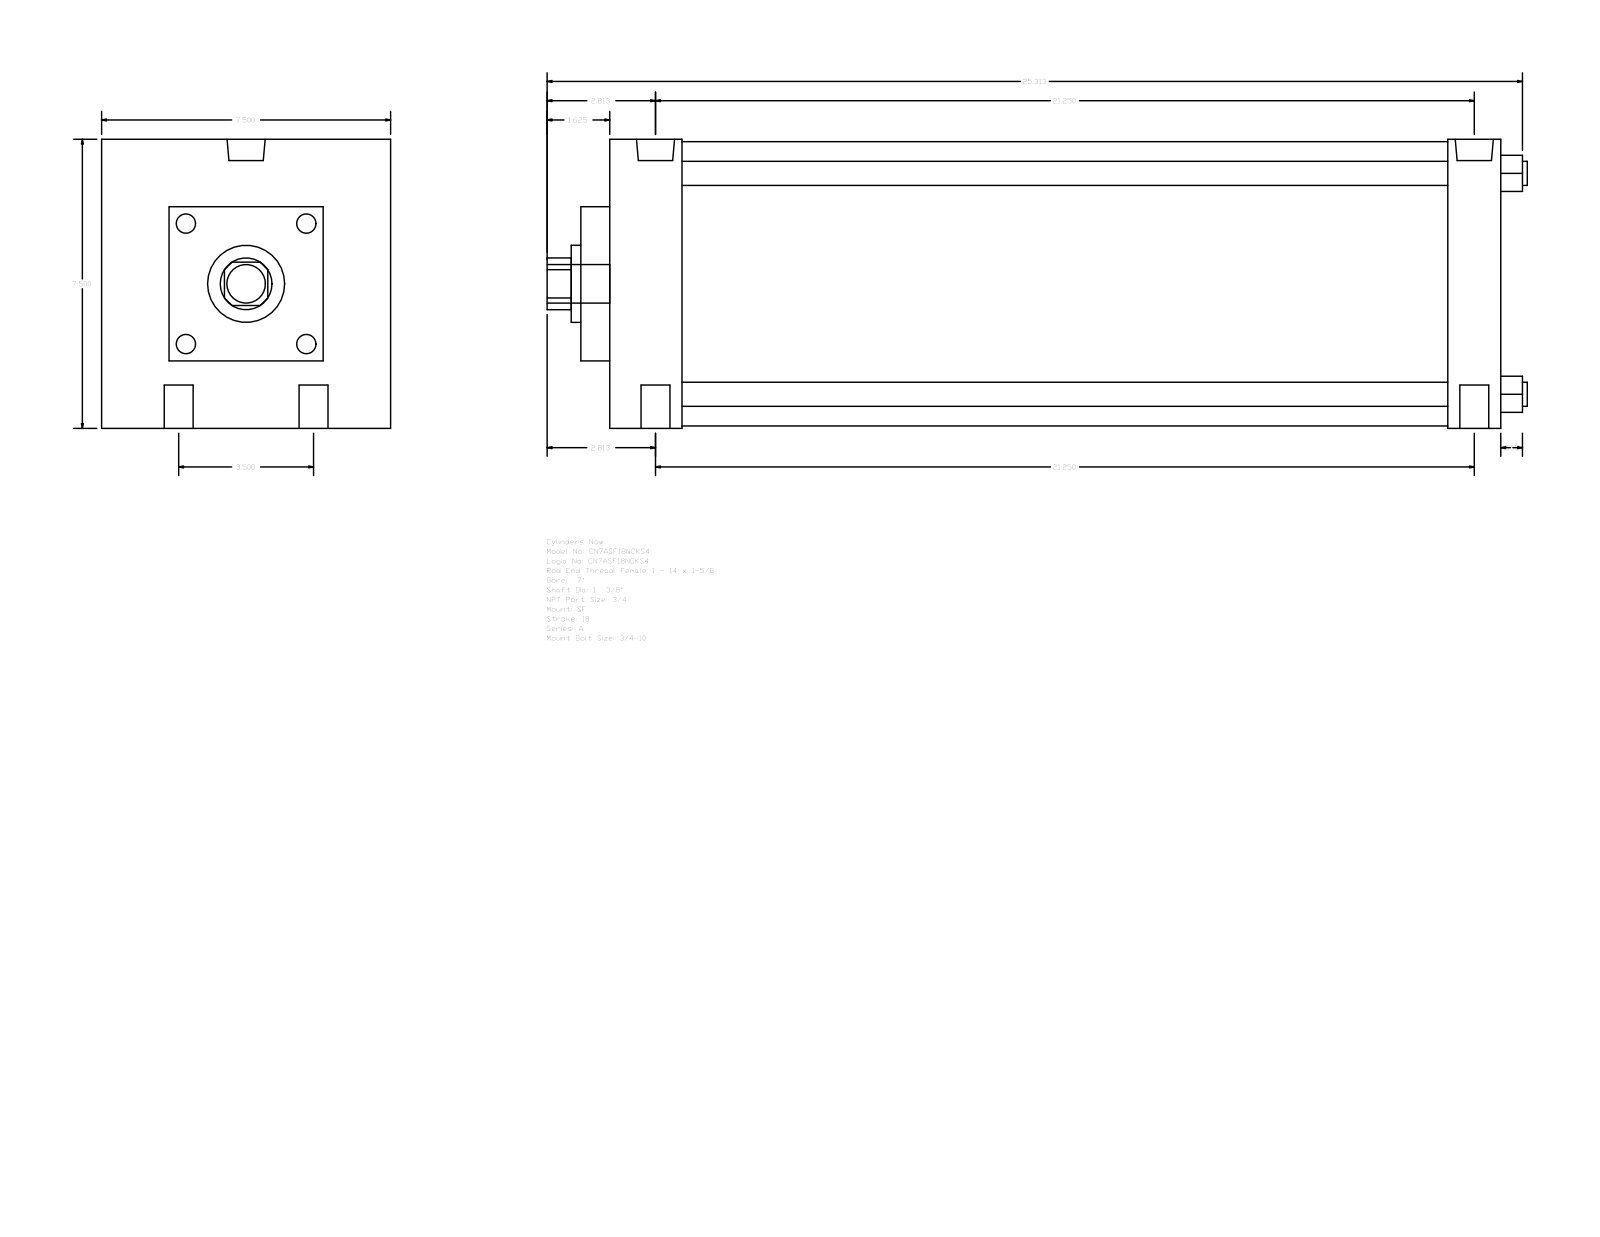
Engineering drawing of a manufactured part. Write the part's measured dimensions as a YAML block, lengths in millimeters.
part_name: "A_SF__0700_1.375"
step_written_by: "GSSL Pune (CONFIG_CONTROL_DESIGN)"
units: millimeters
bodies: {solids: 0, faces: 93, planar: 67, cylindrical: 26, other: 0}
overall_size: [646.11, 190.5, 190.5]
round_holes:
  - {diameter: 19.05, count: 4}
  - {diameter: 15.08, count: 2}
  - {diameter: 25.12, count: 2}
  - {diameter: 34.92, count: 1}
  - {diameter: 50.8, count: 1}
round_bosses_or_shafts:
  - {diameter: 15.88, count: 4}
  - {diameter: 187.32, count: 1}
  - {diameter: 25.4, count: 1}
partial_cylinders:
  - {radius: 17.06, count: 1}
face_to_face_distances: [190.5, 587.38, 19.04, 606.42, 66.67, 571.5, 47.63, 552.46, 504.83, 539.75]
hole_center_spacings: [44.45, 541.58, 539.75, 88.9, 547.02, 528.63]
